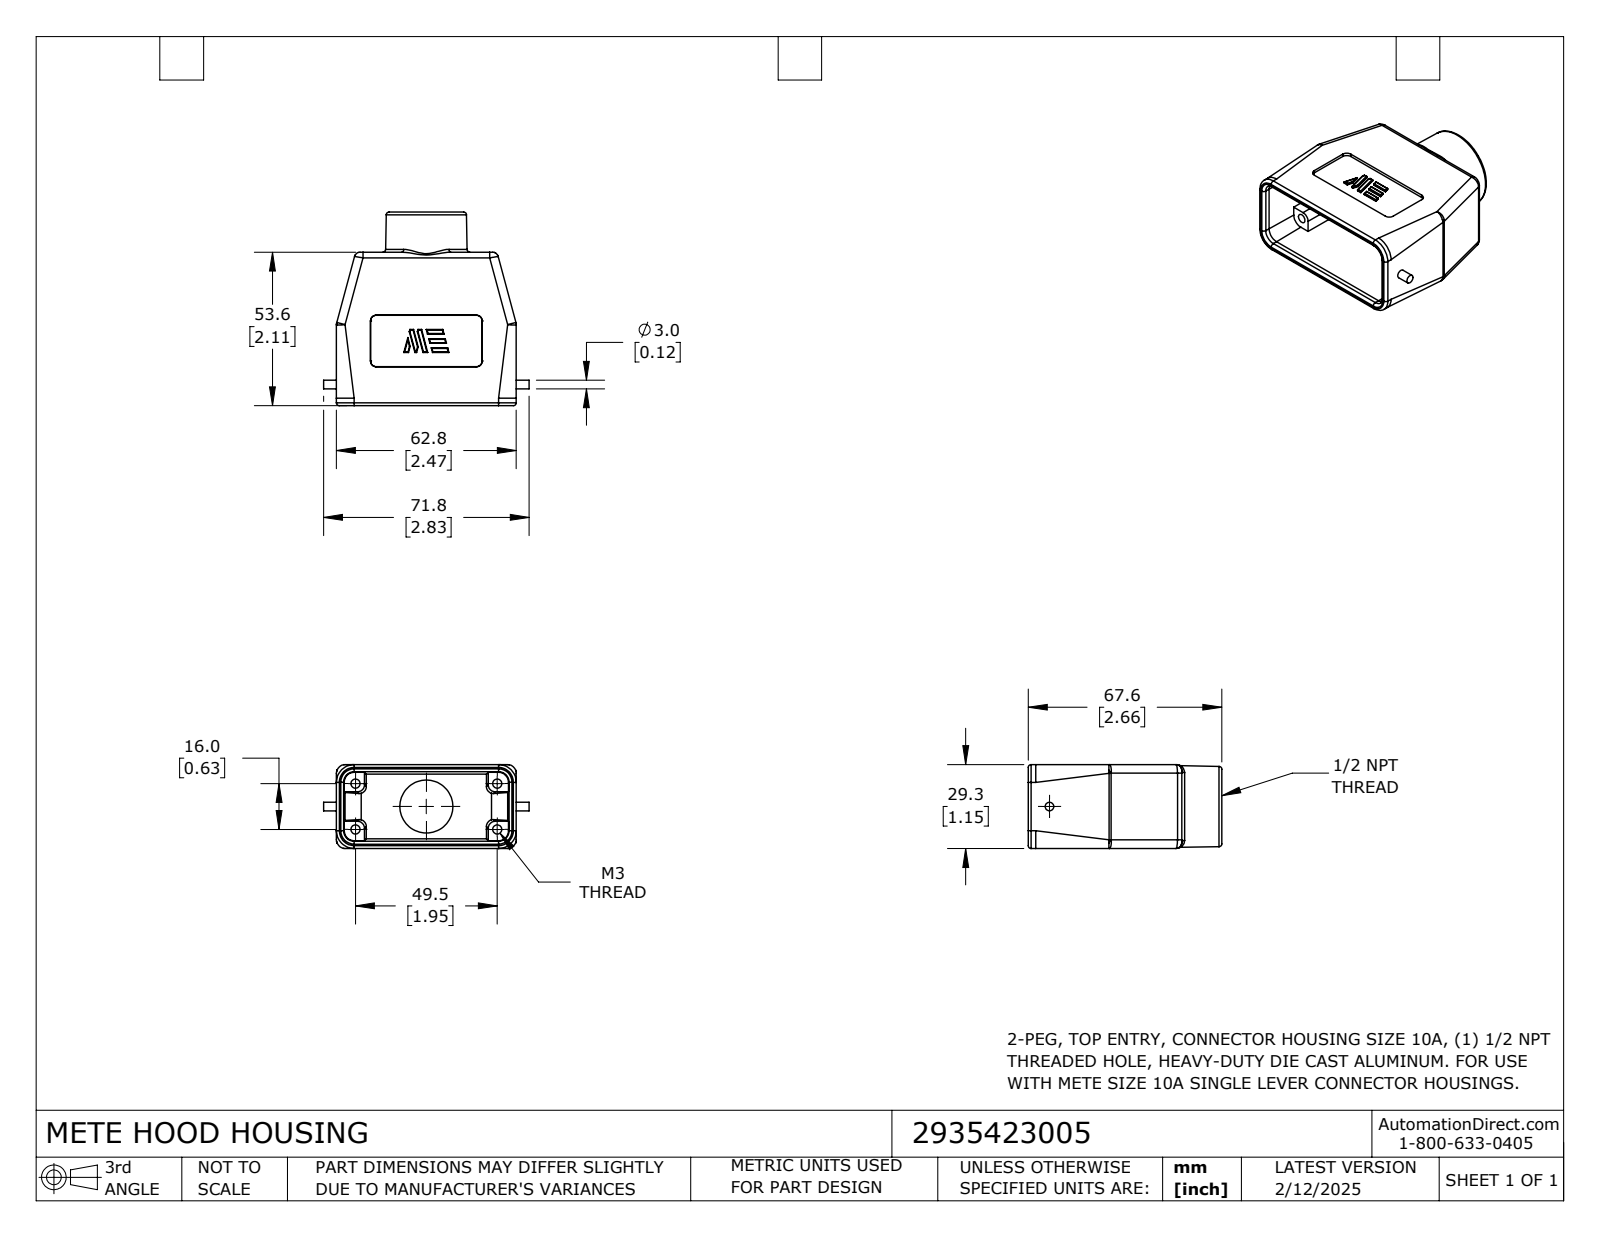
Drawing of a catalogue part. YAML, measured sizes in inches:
part_name: "2935423005"
step_written_by: "SolidWorks 2024 (CONFIG_CONTROL_DESIGN)"
units: inches
bodies: {solids: 1, faces: 261, planar: 116, cylindrical: 96, other: 49}
overall_size: [2.827, 2.661, 1.154]
volume: 2.066
surface_area: 34.57
round_holes:
  - {diameter: 0.126, count: 4}
  - {diameter: 0.728, count: 1}
  - {diameter: 0.827, count: 1}
round_bosses_or_shafts:
  - {diameter: 0.118, count: 1}
partial_cylinders:
  - {radius: 0.008, count: 38}
  - {radius: 0.039, count: 8}
  - {radius: 0.079, count: 4}
  - {radius: 0.098, count: 4}
  - {radius: 0.118, count: 4}
  - {radius: 0.244, count: 4}
  - {radius: 0.114, count: 2}
face_to_face_distances: [1.154, 1.114, 0.039, 0.098, 1.075, 0.279, 2.472, 0.267, 0.02, 0.65]
hole_center_spacings: [1.024, 0.63, 1.949, 2.048]
